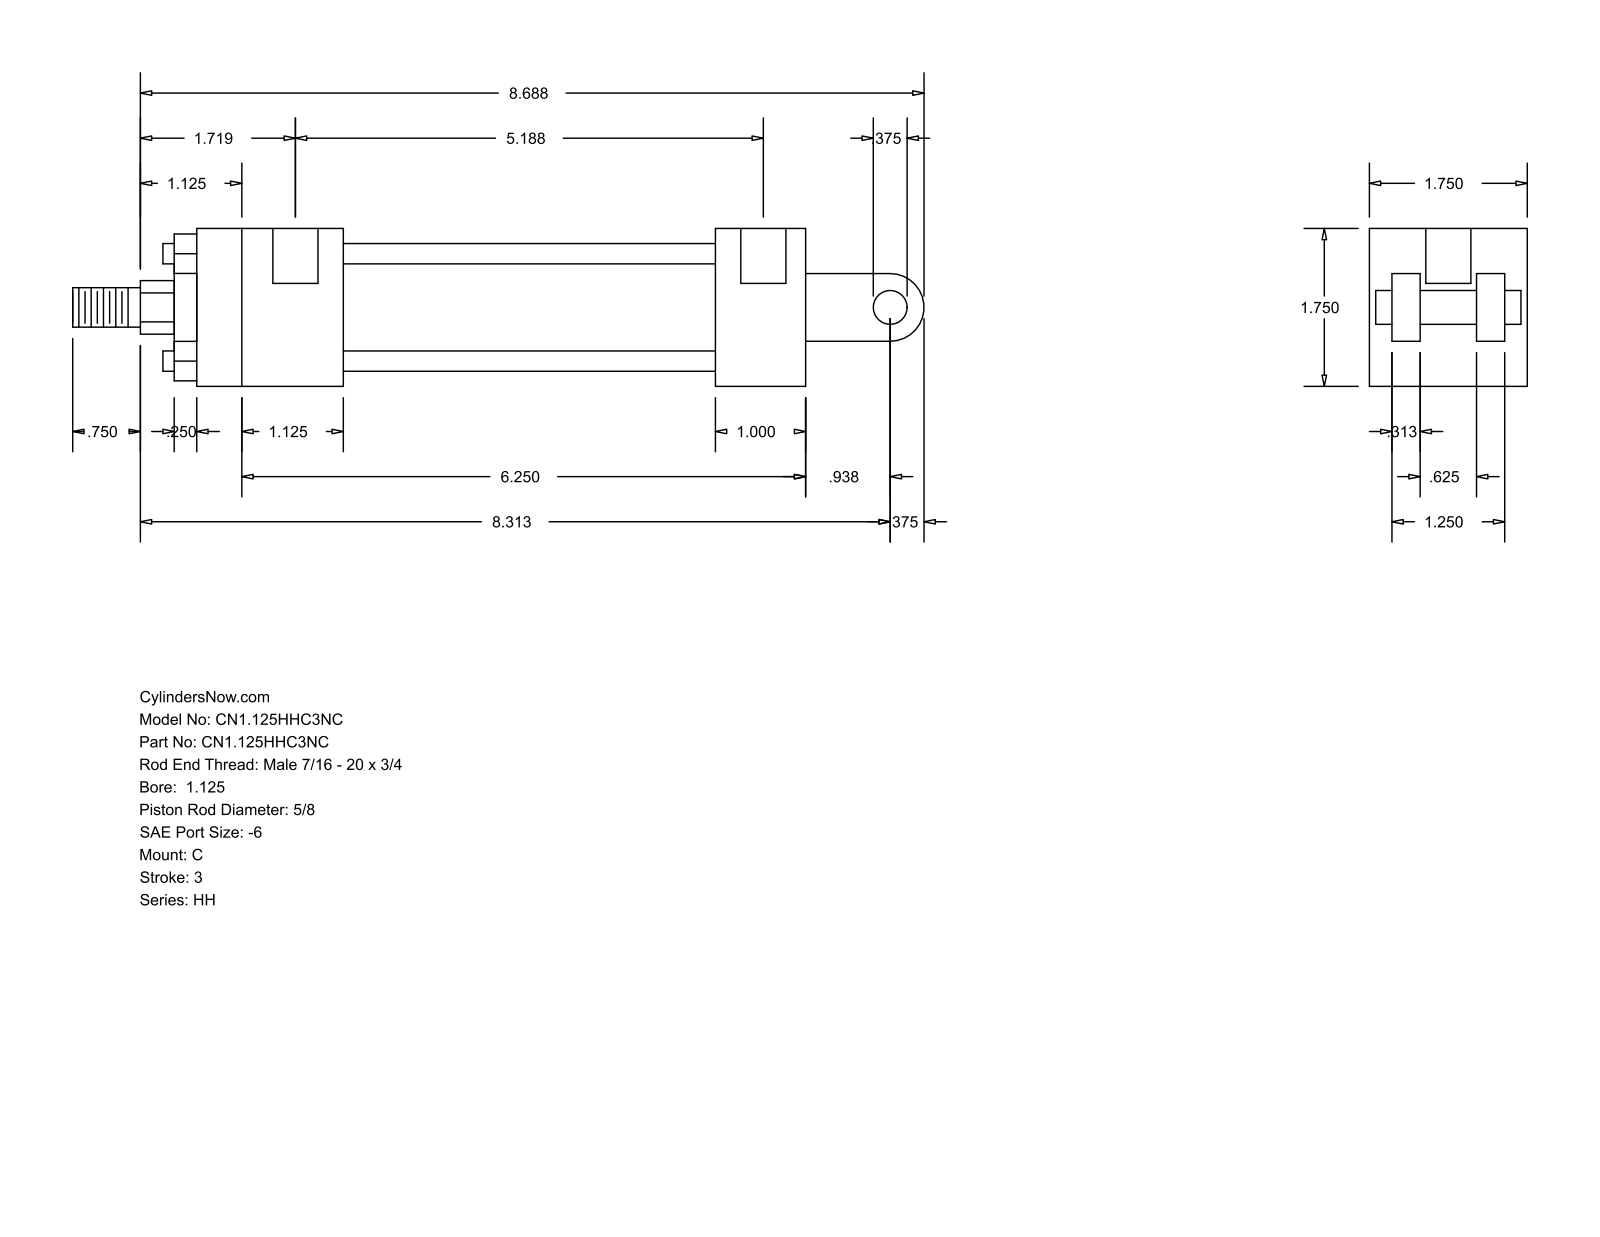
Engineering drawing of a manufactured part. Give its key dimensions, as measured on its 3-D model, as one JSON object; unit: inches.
{"part_name": "HH_C__0112_0.625", "step_written_by": "GSSL Pune (CONFIG_CONTROL_DESIGN)", "units": "inches", "bodies": {"solids": 0, "faces": 99, "planar": 70, "cylindrical": 29, "other": 0}, "overall_size": [9.437, 1.75, 1.75], "round_holes": [[0.219, 4], [0.5, 2]], "round_bosses_or_shafts": [[0.225, 4], [1.375, 1], [1.125, 1], [0.625, 1], [0.437, 1], [0.375, 1]], "partial_cylinders_radius": [[0.297, 1], [0.375, 1]], "face_to_face_distances": [1.75, 0.25, 1.25, 0.563, 1.188, 1.5, 0.313, 0.938, 1.625, 0.5], "hole_center_spacings": [5.063, 0.125, 5.187]}
